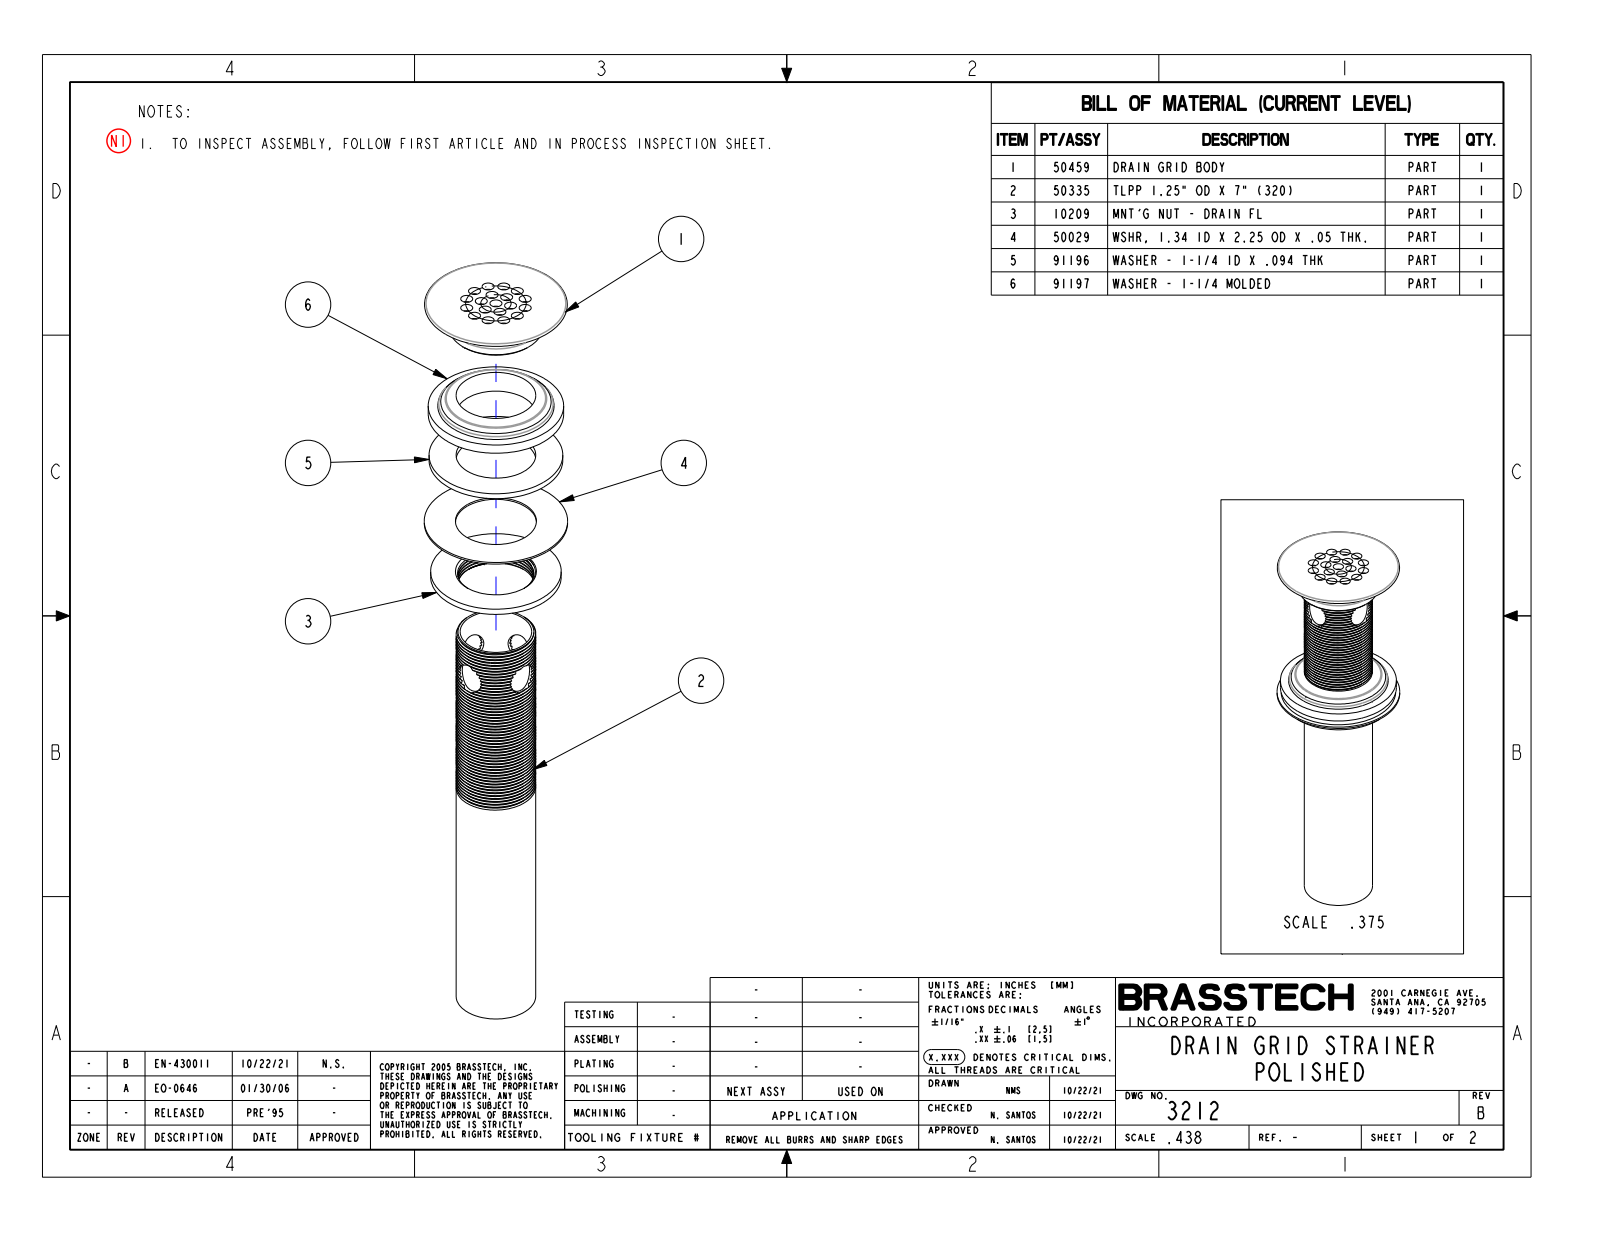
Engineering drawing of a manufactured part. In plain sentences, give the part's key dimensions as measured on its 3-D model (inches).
The part is named "3212". Its 3-D file was written by "CREO PARAMETRIC BY PTC INC, 2018500 (CONFIG_CONTROL_DESIGN)". It is 6 solids with 594 faces: 33 planar, 381 cylindrical and 180 other. Overall it measures 7.16 by 2.25 by 2.25 inches. Its volume is 7.145 cubic inches and its surface area 141.9 square inches. Round holes: 19 of diameter 0.188, 2 of diameter 0.477, 1 of diameter 1.123, 1 of diameter 1.19, 1 of diameter 1.19, 1 of diameter 1.27. Round bosses or shafts: 1 of diameter 2.25, 1 of diameter 2.125, 1 of diameter 2.1, 1 of diameter 2.05, 1 of diameter 1.46, 1 of diameter 1.25, 1 of diameter 1.16. Partial cylindrical surfaces (rounded edges, fillets, slot ends): 6 of radius 0.13. The main face-to-face distances are 0.2, 0.4, 2.56, 0.3, 2.26, 0.5, 0.33, 0.03, 2.23, 2.06. The hole center spacings are 0.475, 0.672, 0.238, 0.246, 0.294, 0.411, 0.531, 0.691.
